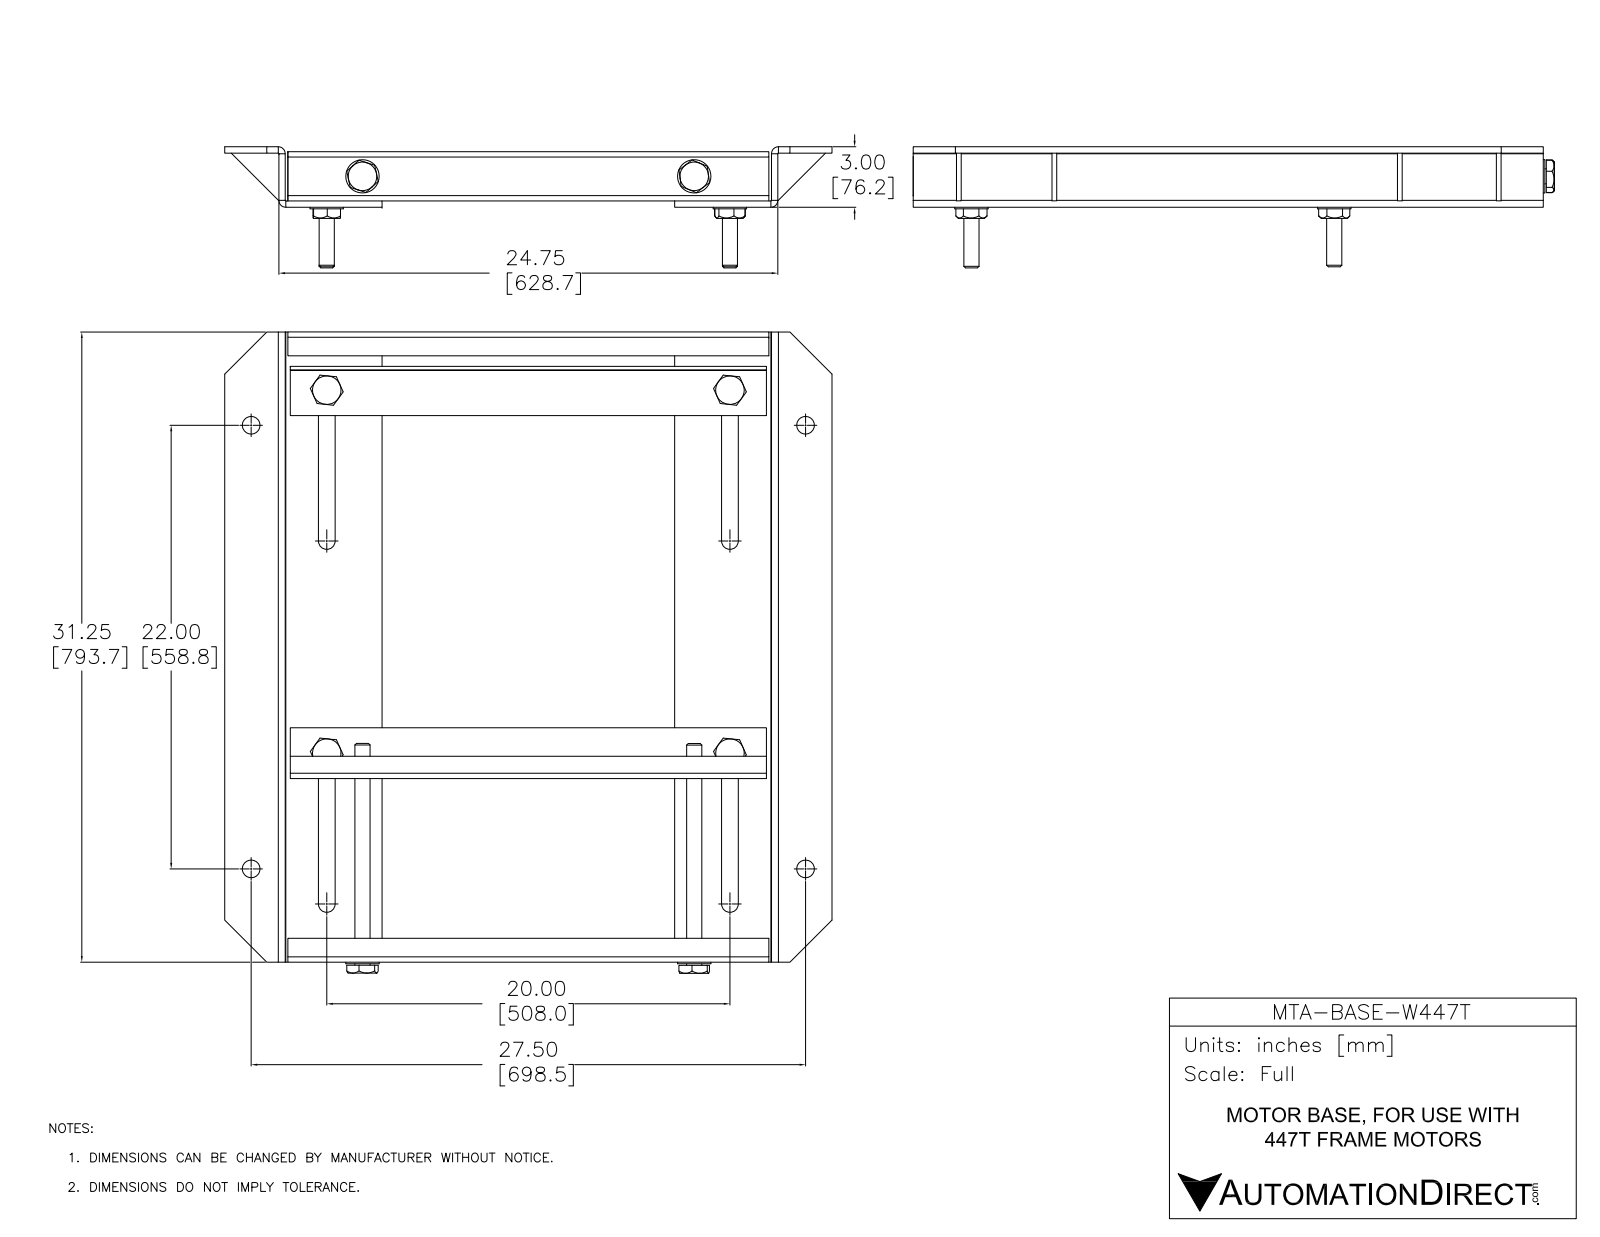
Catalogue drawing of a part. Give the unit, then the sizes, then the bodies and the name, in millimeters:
Units: millimetres
Overall size (bounding box): 807.8 × 765.2 × 152.6
Round holes (diameter × count): ⌀19.1 ×6, ⌀20 ×6, ⌀19.1 ×4, ⌀22 ×2, ⌀22.2 ×2, ⌀22.2 ×2
Round bosses / shafts (diameter × count): ⌀42 ×6
Partial cylindrical surfaces — rounded edges, fillets, slot ends (radius × count): R0.7 ×11, R10.5 ×8, R6.7 ×6, R8.7 ×4, R5.2 ×1
Main face-to-face distances: 8, 68.2, 6, 60.2, 76.2, 620.6, 56, 4.5, 14, 54.2
Hole centre spacings: 105, 174.2, 423.8, 457.2, 508, 558.8, 604.9, 610.5
Volume: 5 209 000 mm³ · Surface area: 1 586 000 mm²
Bodies: 34 solids, 418 faces (240 planar, 110 cylindrical, 68 other)
Part name (STEP PRODUCT): W447T
STEP written by: SolidWorks 2017 (AUTOMOTIVE_DESIGN)
